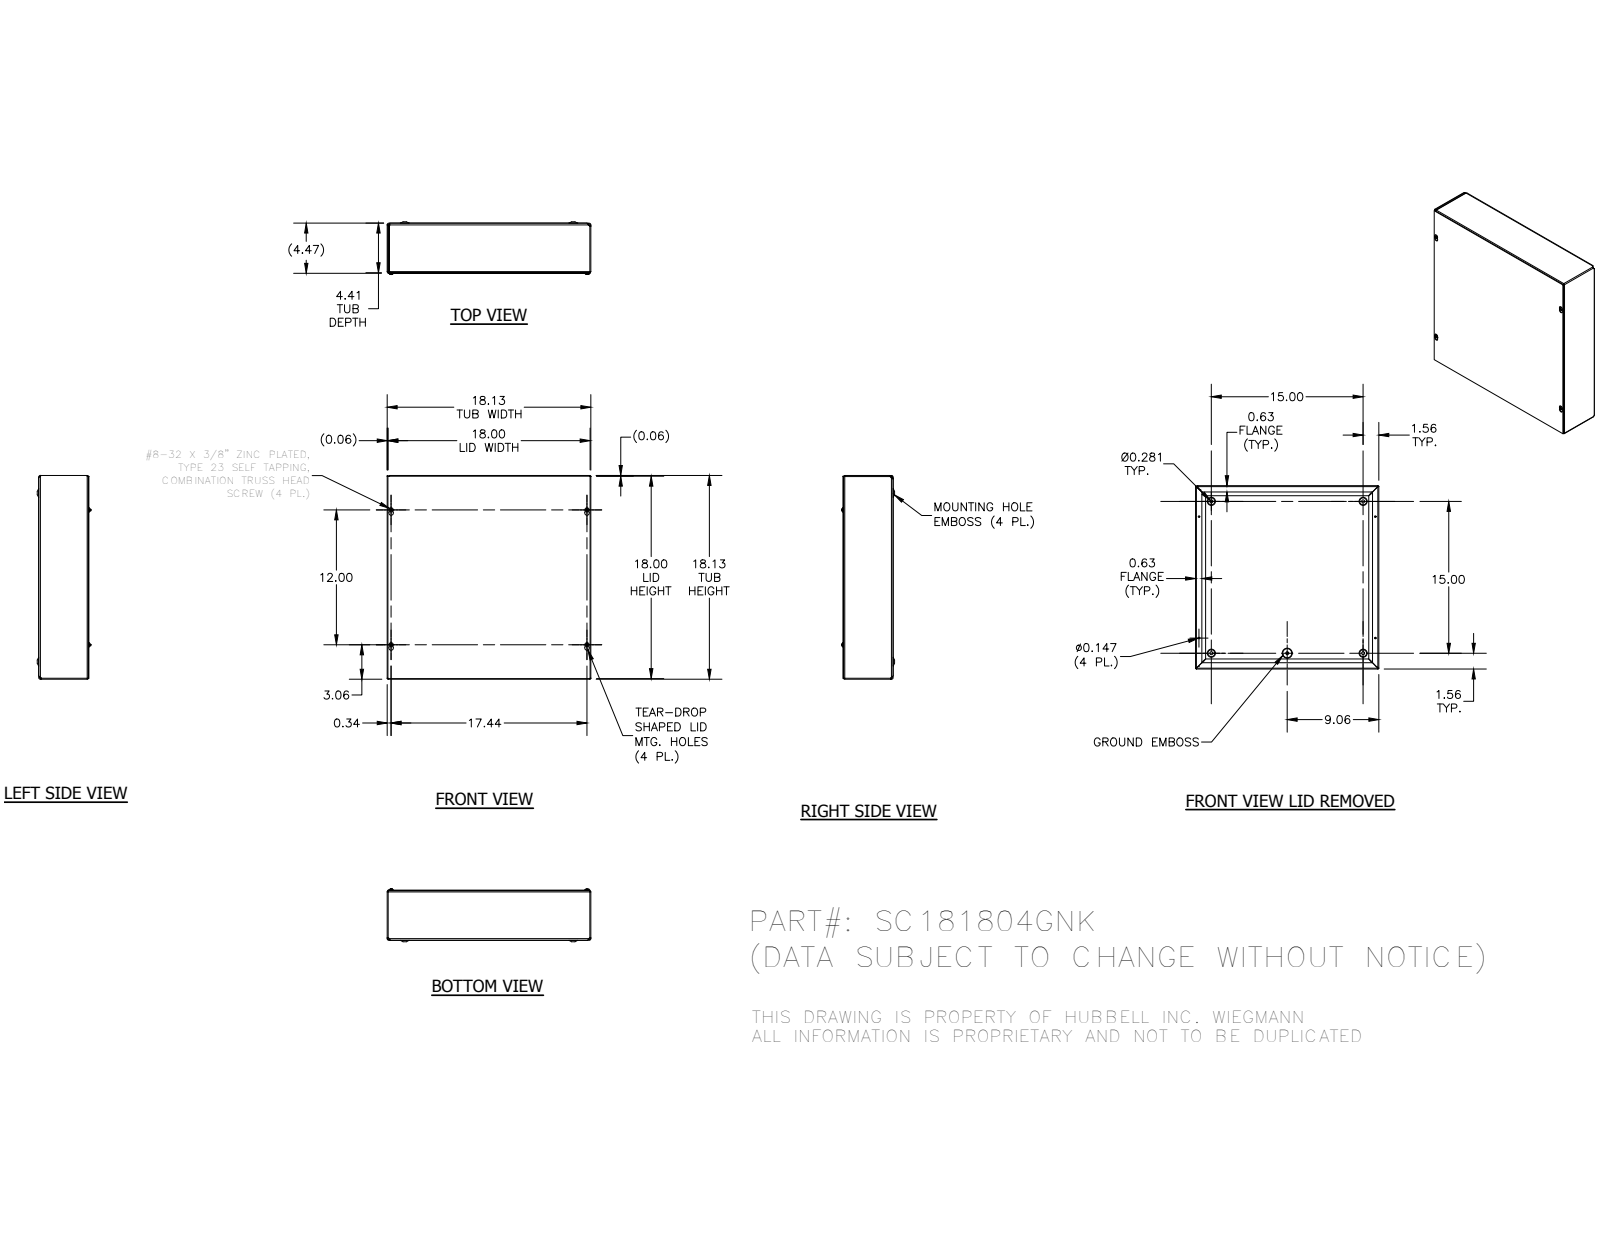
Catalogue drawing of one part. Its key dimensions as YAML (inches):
part_name: "SC1818GNKBKP; SC181804GNKWRA; SC1818GNKLID; 34056 (+1 more)"
step_written_by: "Autodesk Inventor 2014 (AUTOMOTIVE_DESIGN)"
units: inches
bodies: {solids: 7, faces: 358, planar: 133, cylindrical: 73, other: 152}
overall_size: [18.125, 18.125, 4.693]
volume: 65.48
surface_area: 2128
round_holes:
  - {diameter: 0.147, count: 4}
  - {diameter: 0.3, count: 4}
  - {diameter: 0.165, count: 1}
round_bosses_or_shafts:
  - {diameter: 0.384, count: 4}
  - {diameter: 0.164, count: 4}
  - {diameter: 0.228, count: 1}
partial_cylinders:
  - {radius: 0.031, count: 8}
  - {radius: 0.093, count: 8}
  - {radius: 0.055, count: 4}
  - {radius: 0.062, count: 4}
  - {radius: 0.094, count: 4}
  - {radius: 0.117, count: 4}
  - {radius: 0.124, count: 4}
  - {radius: 0.125, count: 4}
face_to_face_distances: [0.062, 4.343, 4.405, 0.063, 4.406, 4.468, 18.063, 18.001, 0.062, 18.125]
hole_center_spacings: [15, 7.5, 12, 13.554, 13.556, 16.288, 16.288, 16.77]
